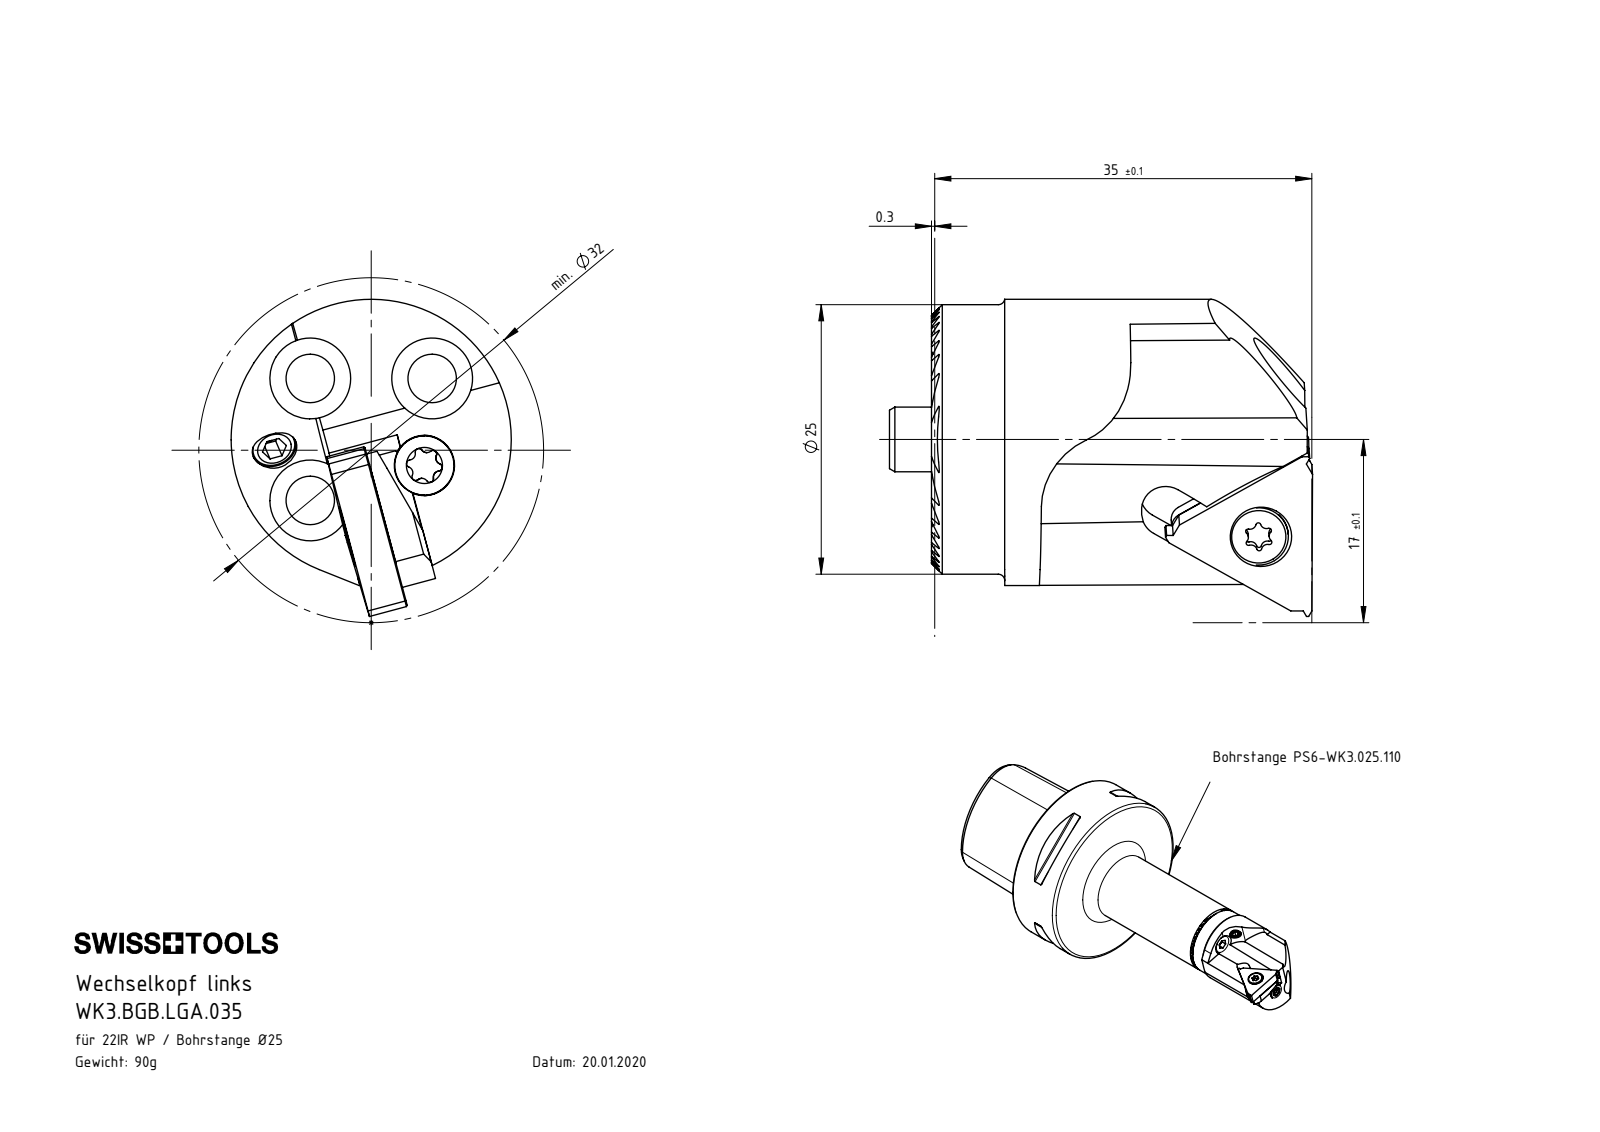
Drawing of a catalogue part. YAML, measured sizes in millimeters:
part_name: "WK3-ER1.001.006_A_Fertigbearbeitung; WKX-ER1.004.005_A_PreviewCfg; WGB-ER2.001.012_A; WK3.BGB.LGA.035 (+5 more)"
step_written_by: "SolidWorks 2017 (AUTOMOTIVE_DESIGN)"
units: millimeters
bodies: {solids: 9, faces: 353, planar: 201, cylindrical: 99, other: 53}
overall_size: [39.27, 29.42, 26]
volume: 11391
surface_area: 7175
round_holes:
  - {diameter: 4.5, count: 3}
  - {diameter: 7.5, count: 3}
  - {diameter: 2.58, count: 2}
  - {diameter: 4.2, count: 2}
  - {diameter: 1.7, count: 1}
  - {diameter: 2.38, count: 1}
  - {diameter: 2.5, count: 1}
  - {diameter: 3, count: 1}
  - {diameter: 3.3, count: 1}
  - {diameter: 4, count: 1}
  - {diameter: 4.02, count: 1}
  - {diameter: 6, count: 1}
round_bosses_or_shafts:
  - {diameter: 5.5, count: 2}
  - {diameter: 3, count: 2}
  - {diameter: 26, count: 1}
  - {diameter: 25, count: 1}
  - {diameter: 4, count: 1}
  - {diameter: 3.18, count: 1}
  - {diameter: 2.78, count: 1}
partial_cylinders:
  - {radius: 0.12, count: 20}
  - {radius: 0.23, count: 6}
  - {radius: 0.34, count: 6}
  - {radius: 0.57, count: 6}
  - {radius: 0.57, count: 6}
  - {radius: 0.1, count: 2}
  - {radius: 7, count: 2}
  - {radius: 0.25, count: 1}
face_to_face_distances: [4.33, 1.08, 3.25, 5.41, 8.66, 7.58, 2.17, 2.16, 6.55, 6.5]
hole_center_spacings: [8, 11.32, 16.01, 279.88, 279.93]
